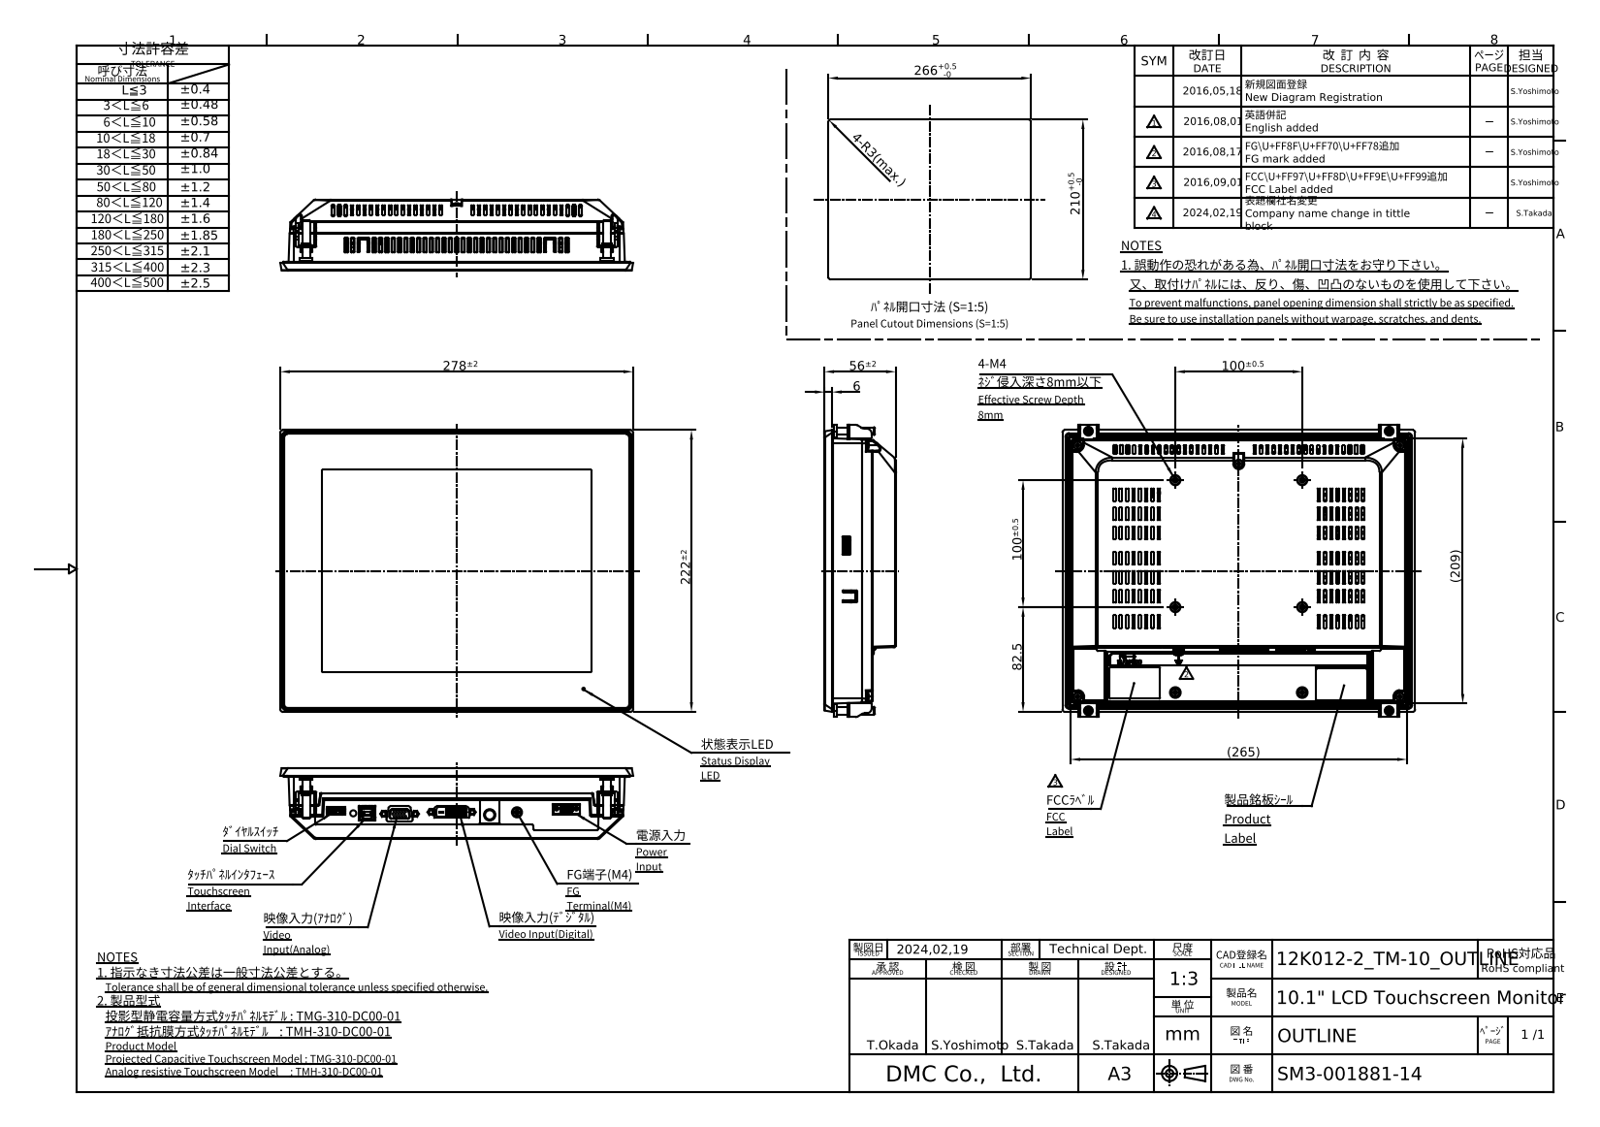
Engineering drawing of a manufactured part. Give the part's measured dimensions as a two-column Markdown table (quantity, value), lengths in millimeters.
| quantity | value |
| --- | --- |
| part name | HP_TMG(H)-310-DC00-01 |
| STEP written by | Autodesk Inventor 2017 (CONFIG_CONTROL_DESIGN) |
| units | millimeters |
| bodies | 5 solids, 6545 faces (3812 planar, 1189 cylindrical, 1544 other) |
| overall size | 278 × 230.29 × 56 |
| volume | 545 177 mm³ |
| surface area | 604 608 mm² |
| round holes (diameter × count) | 3.5 × 122, 3 × 32, 8 × 22, 1 × 21, 4 × 10, 3.2 × 7, 4.5 × 6, 1.6 × 4, 2.6 × 4, 3.8 × 4, 9 × 4, 4.8 × 3 |
| round bosses / shafts (diameter × count) | 6.15 × 12, 3 × 11, 3.6 × 10, 4 × 9, 6.2 × 8, 7.15 × 5, 10 × 4, 7 × 4 |
| partial cylindrical surfaces (radius × count) | 0.5 × 190, 1 × 120, 0.3 × 97, 1.3 × 18, 0.1 × 13, 0.8 × 13, 1.1 × 13, 1.6 × 12 |
| main face-to-face distances | 1, 27.7, 20.1, 3, 19, 1.1, 21.1, 20, 7, 28.7 |
| hole center spacings | 2.29, 3.96, 6.05, 2.28, 4.58, 4.57, 3.97, 6.87 |
